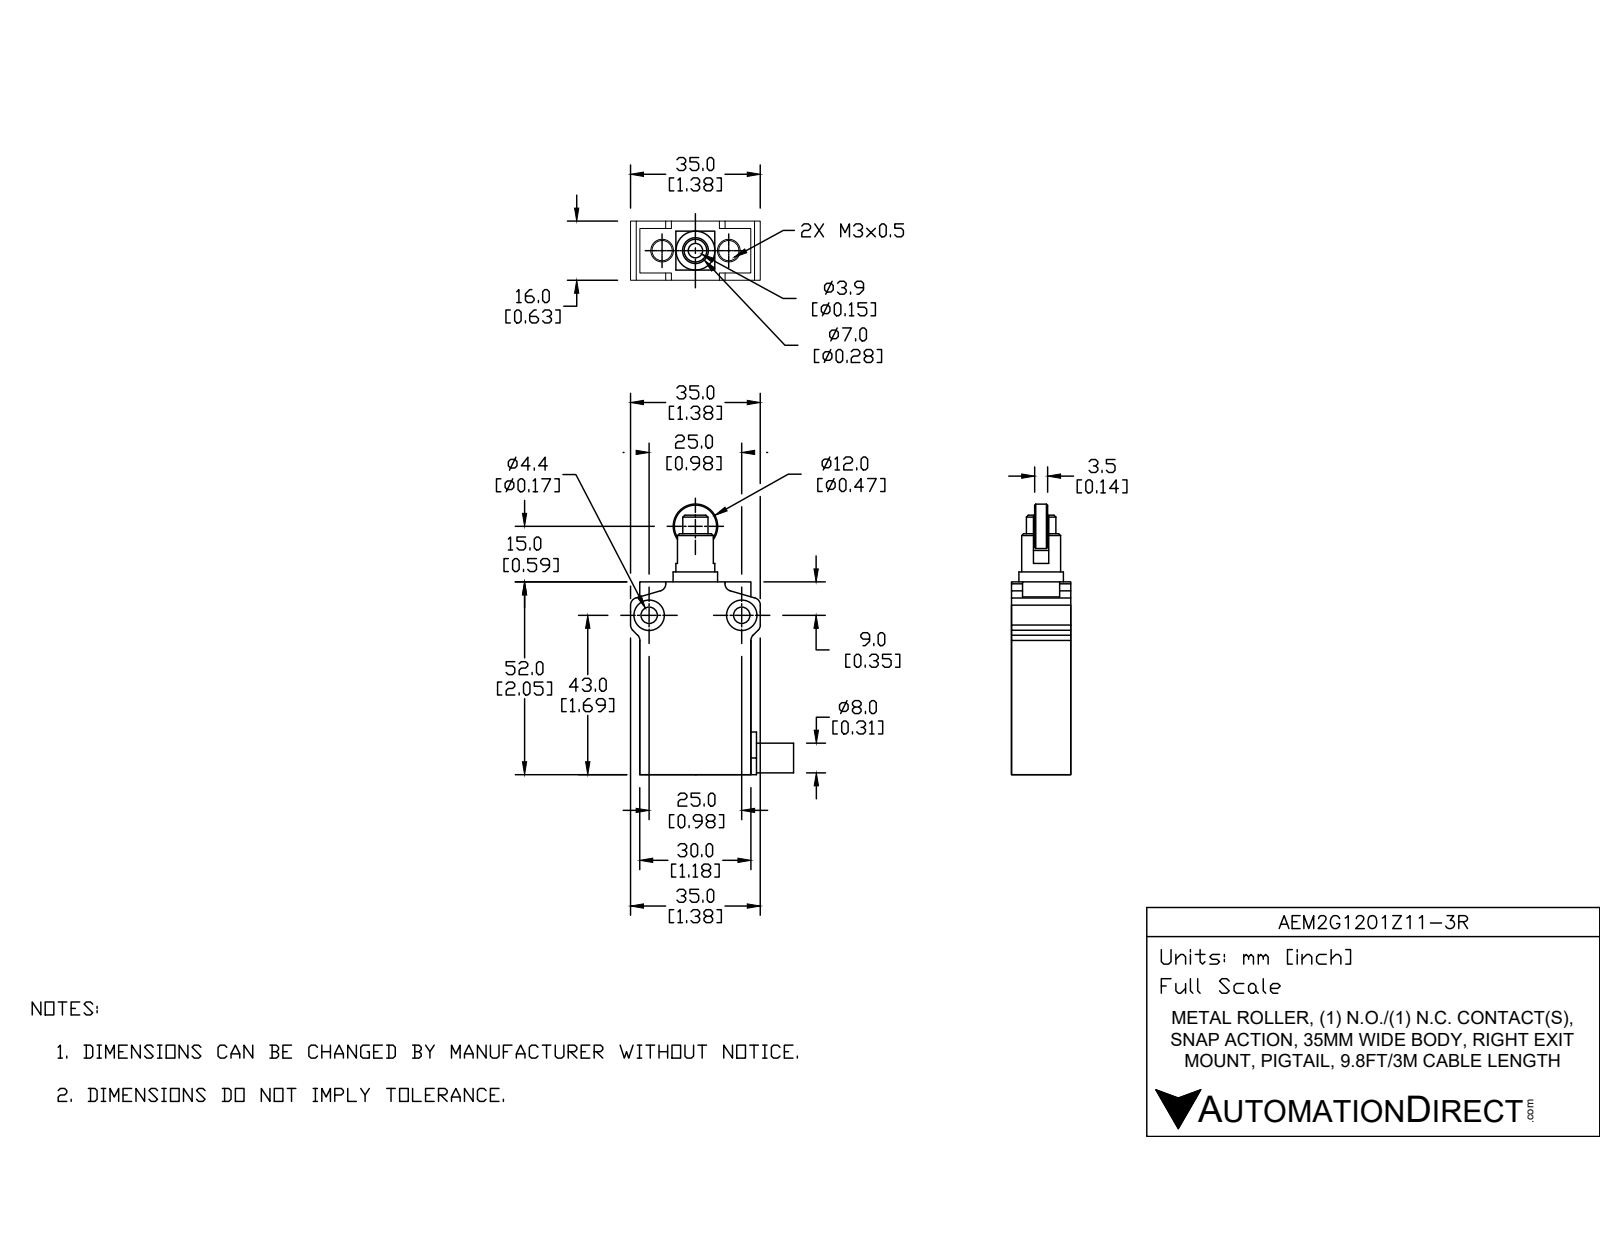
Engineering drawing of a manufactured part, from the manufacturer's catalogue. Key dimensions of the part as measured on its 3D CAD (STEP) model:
Part name (STEP PRODUCT): AEM2G1201Z11-3R
STEP written by: SolidWorks 2017 (AUTOMOTIVE_DESIGN)
Units: inches
Bodies: 5 solids, 129 faces (64 planar, 52 cylindrical, 13 other)
Overall size (bounding box): 2.756 × 1.87 × 0.63
Volume: 1.516 in³ · Surface area: 14.04 in²
Round holes (diameter × count): ⌀0.118 ×2, ⌀0.173 ×2, ⌀0.323 ×2, ⌀0.317 ×1
Round bosses / shafts (diameter × count): ⌀0.472 ×2, ⌀0.413 ×1, ⌀0.323 ×1, ⌀0.313 ×1, ⌀0.22 ×1
Partial cylindrical surfaces — rounded edges, fillets, slot ends (radius × count): R0.079 ×8, R0.256 ×1
Main face-to-face distances: 0.63, 1.181, 1.929, 0.472, 1.74, 0.189, 0.234, 0.15, 0.157, 0.238
Hole centre spacings: 0.374, 0.748, 0.984
